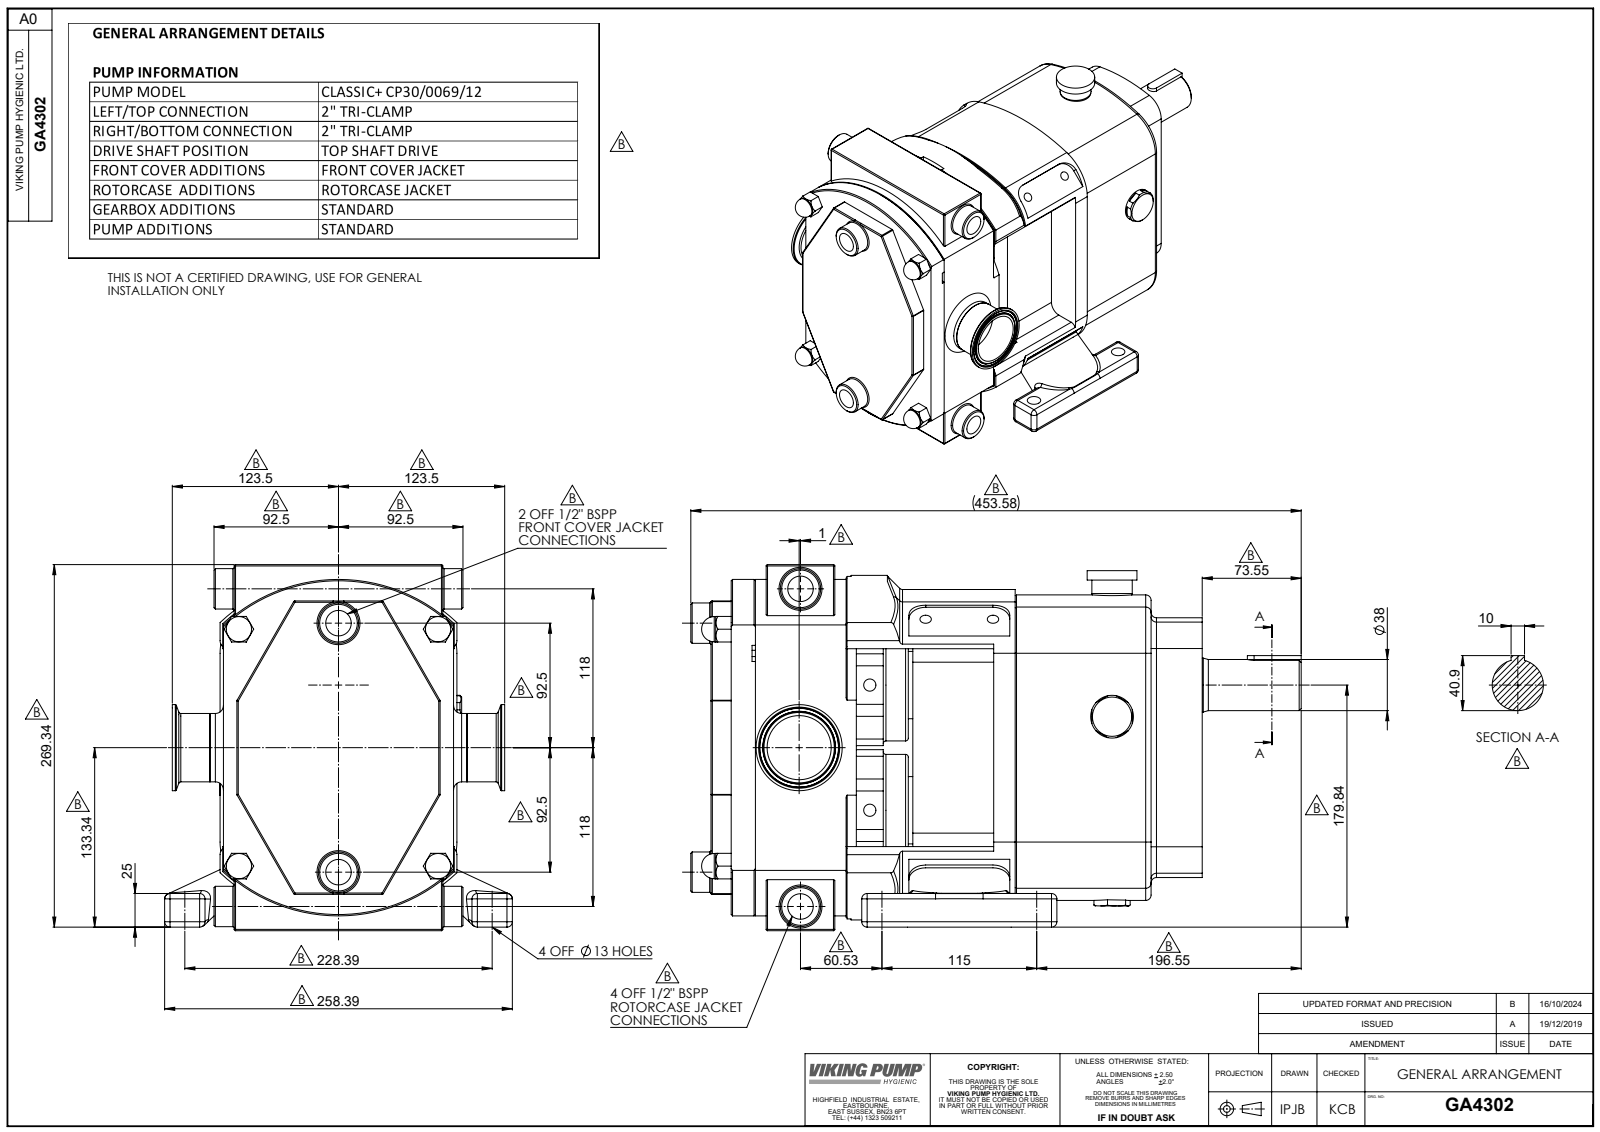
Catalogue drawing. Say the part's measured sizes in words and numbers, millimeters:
The part is named "GA4302; Copy of Z94-5121-33 - 2 INCH^GA4302; Copy of MP30 Half Inch BSP Jacket^GA4302; Copy of MP30S Half Inch Jacket^GA4302 (+1 more)". Its 3-D file was written by "SolidWorks 2023 (AUTOMOTIVE_DESIGN)". It is 6 solids with 876 faces: 293 planar, 298 cylindrical and 285 other. Overall it measures 453.58 by 272 by 258.38 millimeters. Its volume is 12 200 000 cubic millimeters and its surface area 654 199 square millimeters. Round holes: 4 of diameter 8.5, 4 of diameter 10.11, 4 of diameter 13, 4 of diameter 18.97, 2 of diameter 9.09, 1 of diameter 35, 1 of diameter 47.65. Round bosses or shafts: 5 of diameter 30, 4 of diameter 18.8, 2 of diameter 83, 2 of diameter 50, 1 of diameter 64, 1 of diameter 50.8, 1 of diameter 40.01, 1 of diameter 38. Partial cylindrical surfaces (rounded edges, fillets, slot ends): 44 of radius 1, 44 of radius 4, 12 of radius 10, 10 of radius 6, 4 of radius 12.5, 4 of radius 12.57, 4 of radius 12.6, 4 of radius 20. The main face-to-face distances are 1.5, 169.5, 15, 139, 38, 134.98, 149.98, 29, 215.05, 350.03. The hole center spacings are 63.64, 34.84, 50.05, 70.13, 84.07, 88.12, 90, 111.8.
